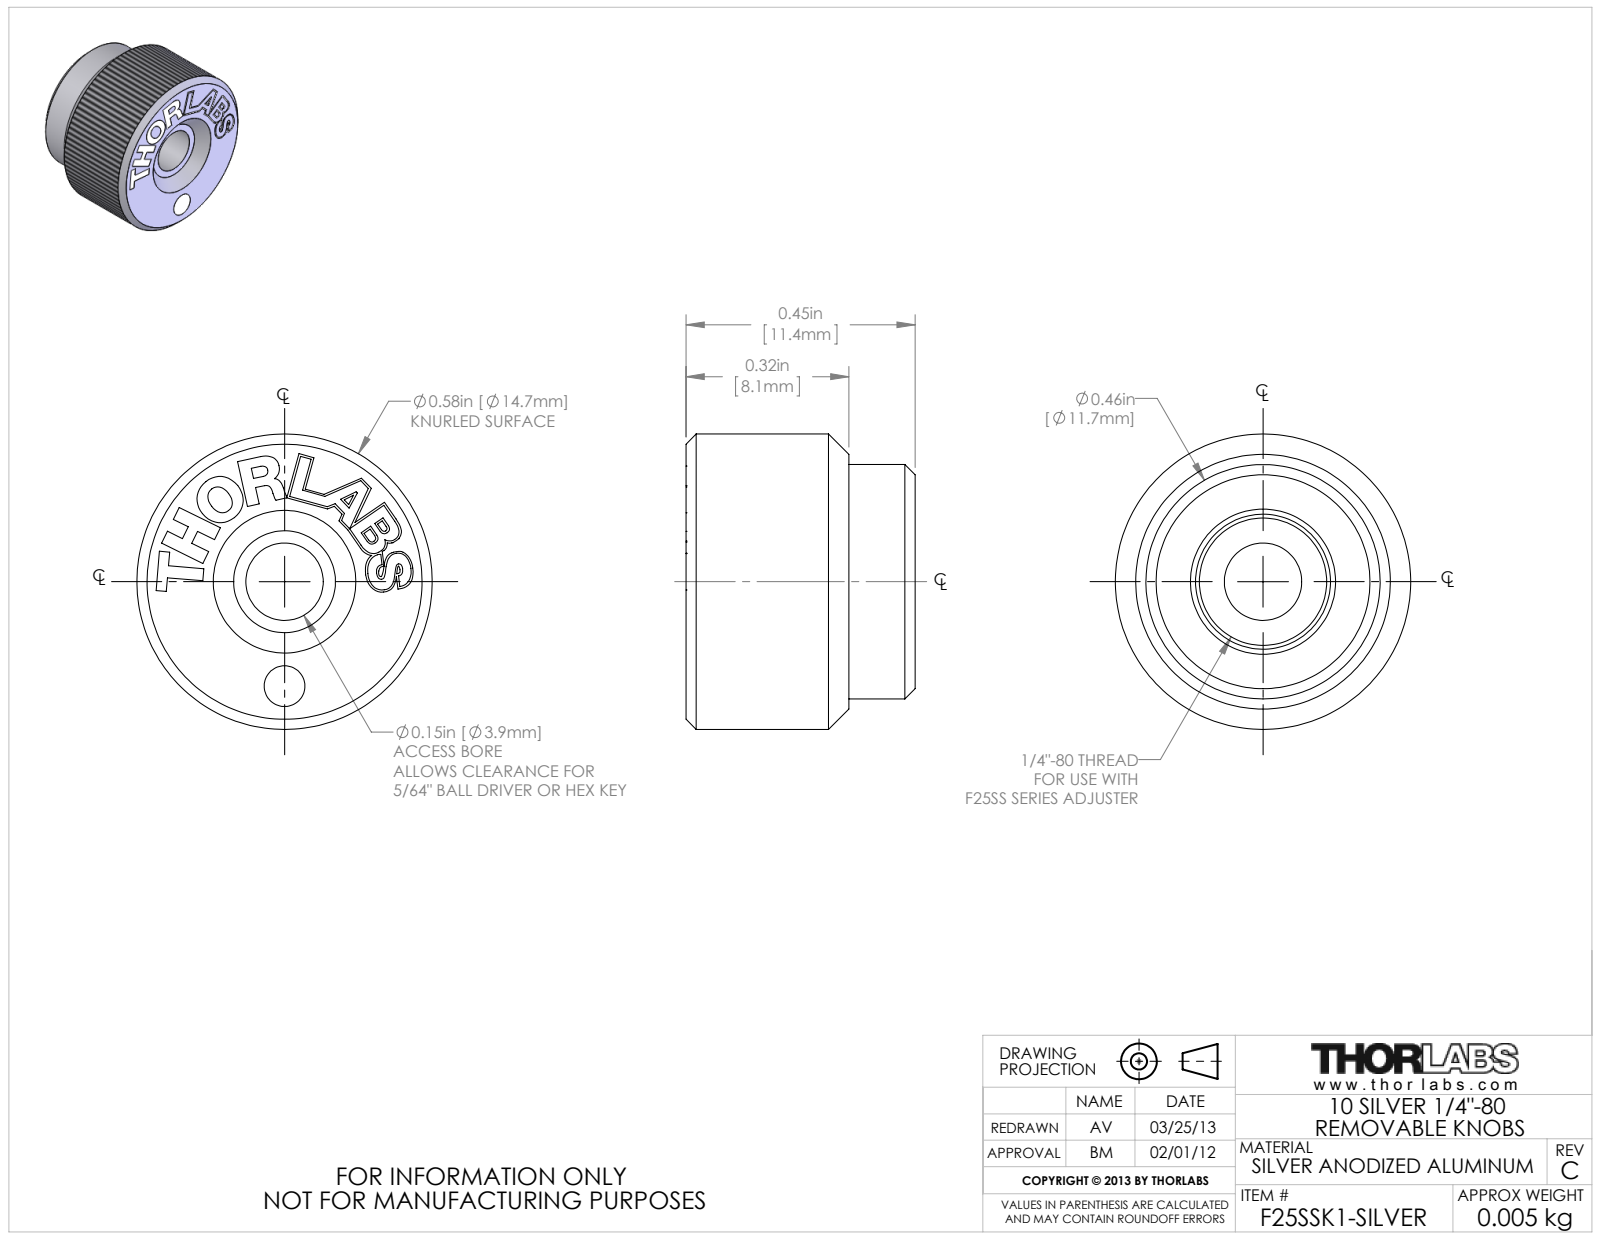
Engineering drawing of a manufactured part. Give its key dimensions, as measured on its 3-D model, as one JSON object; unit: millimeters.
{"part_name": "23394-E0W", "step_written_by": "SolidWorks 2012 (AUTOMOTIVE_DESIGN)", "units": "millimeters", "bodies": {"solids": 1, "faces": 210, "planar": 118, "cylindrical": 21, "other": 71}, "overall_size": [14.7, 14.7, 11.4], "volume_mm3": 1400, "surface_area_mm2": 953, "round_holes": [[2, 1], [3.9, 1], [6.4, 1], [6.7, 1], [7.4, 1]], "round_bosses_or_shafts": [[14.7, 1], [11.7, 1]], "partial_cylinders_radius": [[0.4, 1], [1.2, 1], [1.5, 1]], "face_to_face_distances": [11.4, 6.9, 4.6, 8.1, 1.3, 3.3, 0.5, 7.6, 0.8, 3.8], "hole_center_spacings": [5.2]}
